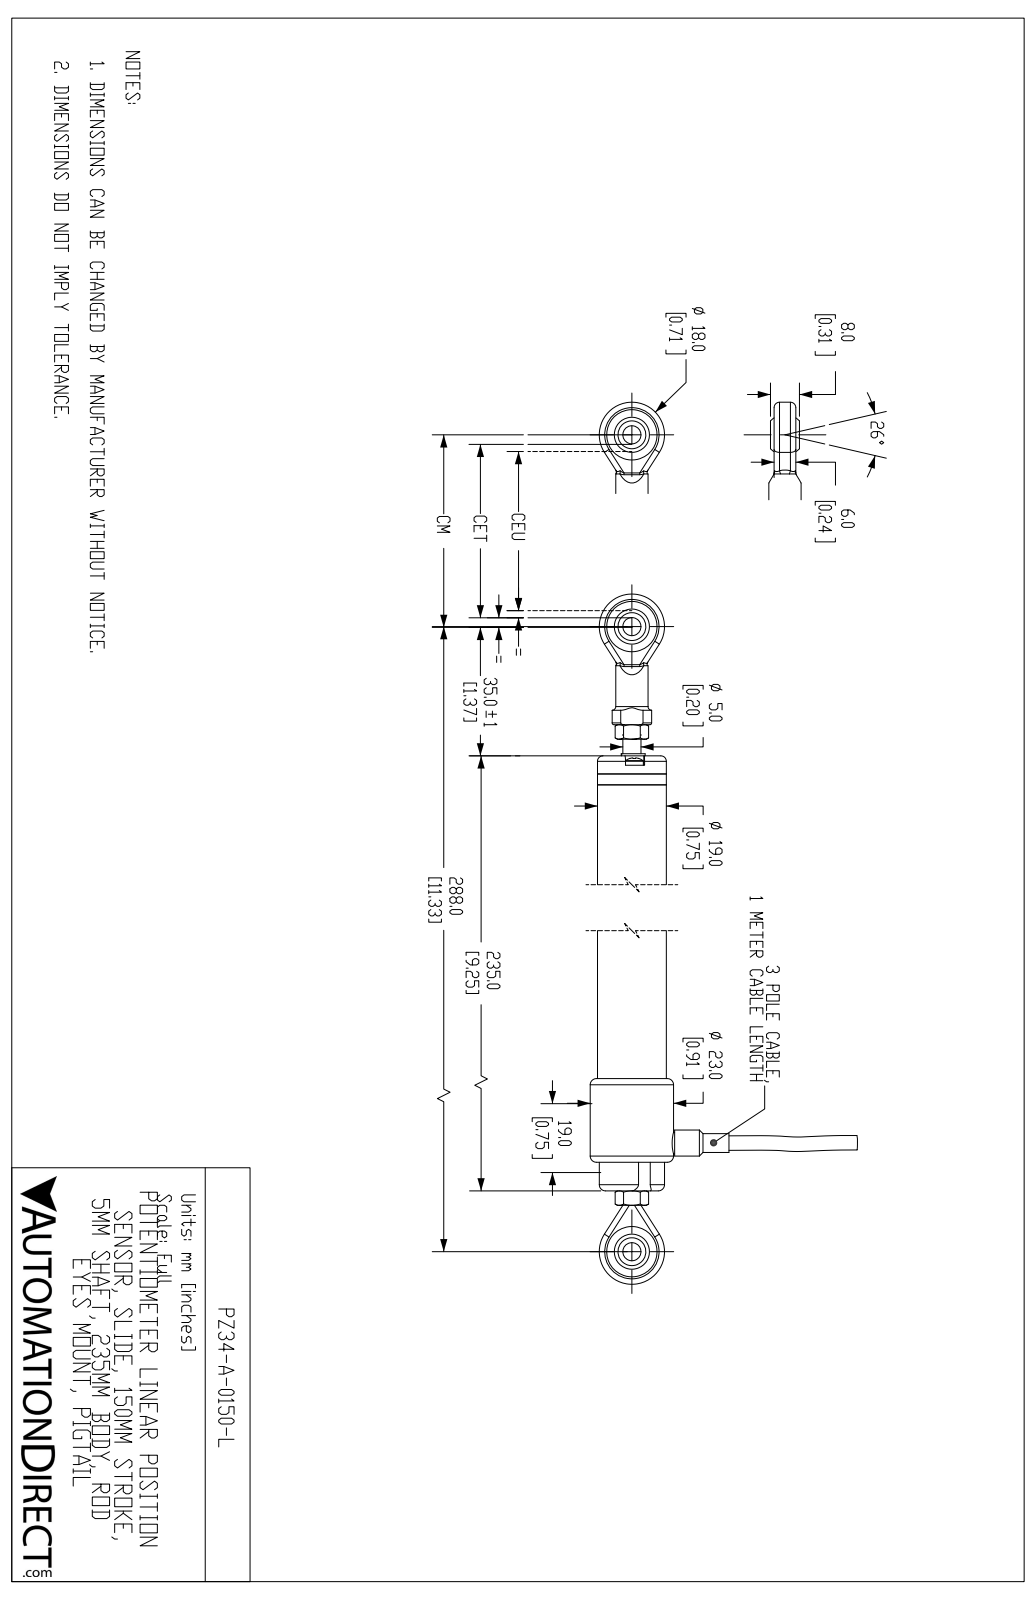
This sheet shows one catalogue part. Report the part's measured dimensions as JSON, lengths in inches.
{"part_name": "PZ34-A-0150-L", "step_written_by": "SolidWorks 2019 (AUTOMOTIVE_DESIGN)", "units": "inches", "bodies": {"solids": 18, "faces": 916, "planar": 334, "cylindrical": 198, "other": 384}, "overall_size": [12.028, 2.904, 0.906], "volume_in3": 4.895, "surface_area_in2": 46.75, "round_holes": [[0.079, 4], [0.114, 4], [0.197, 2], [0.209, 2], [0.547, 2], [0.138, 1], [0.165, 1], [0.24, 1], [0.354, 1], [0.75, 1]], "round_bosses_or_shafts": [[0.197, 5], [0.098, 4], [0.906, 1], [0.748, 1], [0.709, 1], [0.35, 1], [0.283, 1], [0.236, 1]], "partial_cylinders_radius": [[0.059, 8], [0.01, 4], [0.02, 2], [0.039, 2], [0.104, 2], [0.354, 2], [0.017, 1], [0.063, 1]], "face_to_face_distances": [8.346, 8.228, 0.118, 0.315, 0.224, 0.213, 0.217, 0.051, 0.039, 0.264], "hole_center_spacings": [0.269, 0.082, 0.532, 0.539, 11.319]}
